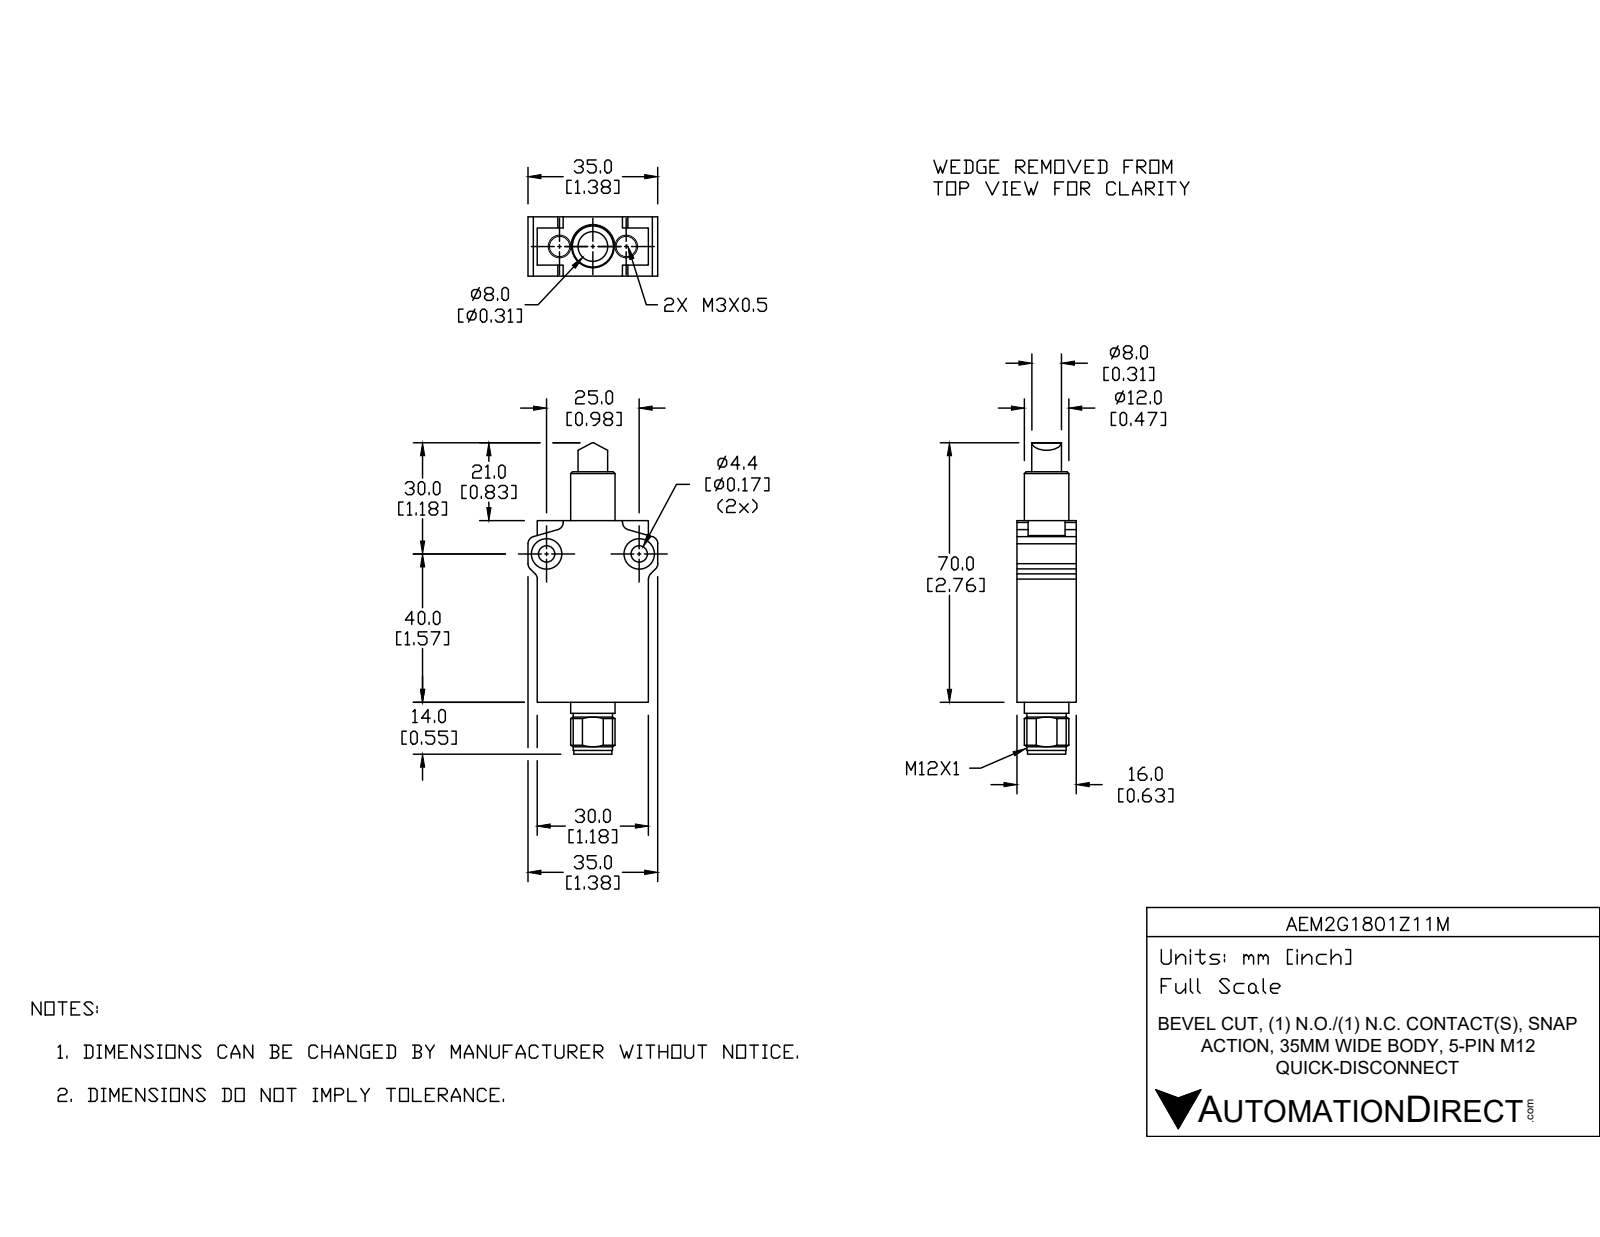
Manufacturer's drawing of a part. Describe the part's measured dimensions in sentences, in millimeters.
The part is named "AEM2G1801Z11M". Its 3-D file was written by "SolidWorks 2017 (AUTOMOTIVE_DESIGN)". It is 3 solids with 152 faces: 52 planar, 65 cylindrical and 35 other. Overall it measures 87 by 35 by 16 millimeters. Its volume is 27 300 cubic millimeters and its surface area 9 219 square millimeters. Round holes: 2 of diameter 3, 2 of diameter 4.4, 2 of diameter 8.2, 1 of diameter 8.1. Round bosses or shafts: 1 of diameter 12, 1 of diameter 10.6, 1 of diameter 10.3, 1 of diameter 8. Partial cylindrical surfaces (rounded edges, fillets, slot ends): 8 of radius 2, 1 of radius 0.8, 1 of radius 6.5. The main face-to-face distances are 16, 30, 12, 52, 47.2, 4.8, 2.5, 32.5, 4, 1. The hole center spacings are 9.5, 19, 25.
